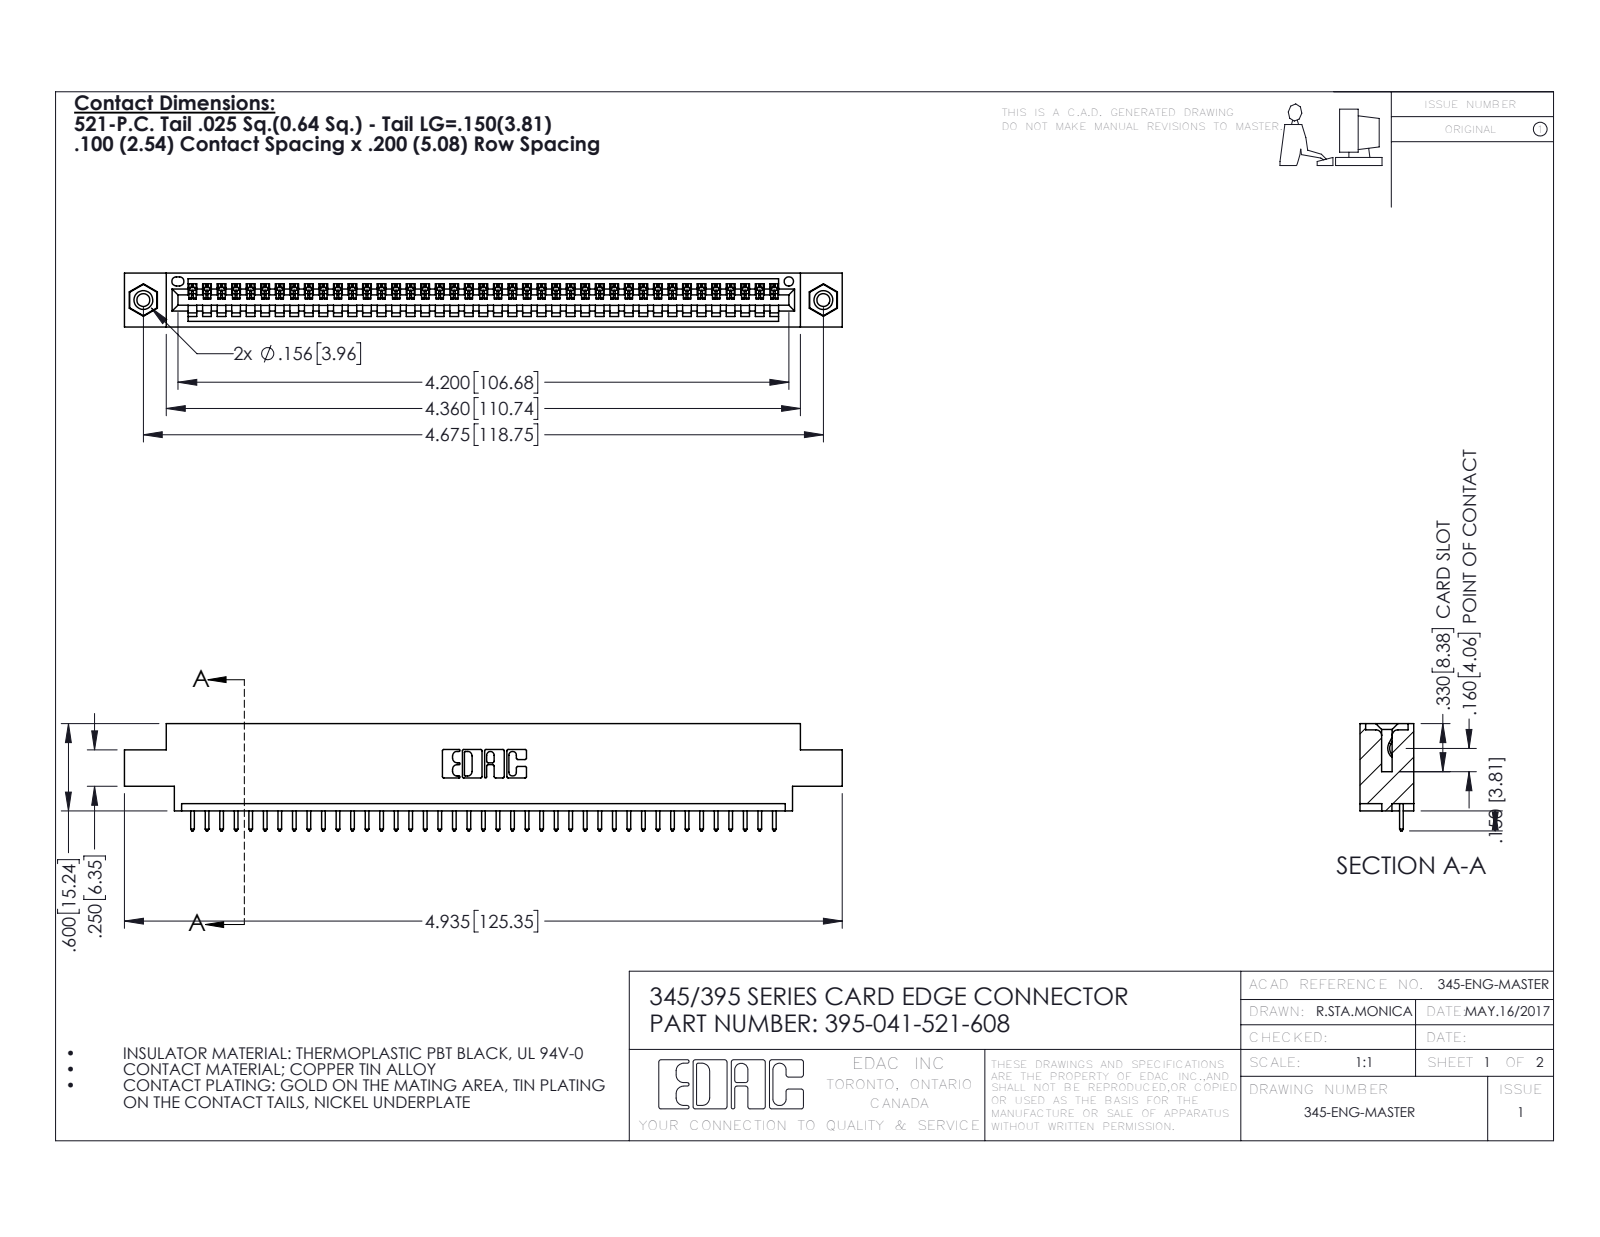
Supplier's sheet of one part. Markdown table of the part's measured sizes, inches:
| quantity | value |
| --- | --- |
| part name | 345-250-001_345-250-003-102; 395-041-521-608; 345 Part_0.170 Offset - 0.156 Dia-TI; 345-292-001_345-293-121 |
| STEP written by | SolidWorks 2016 (CONFIG_CONTROL_DESIGN) |
| units | inches |
| bodies | 44 solids, 2568 faces (1756 planar, 796 cylindrical, 16 other) |
| overall size | 4.935 × 0.737 × 0.37 |
| volume | 0.712 in³ |
| surface area | 23.52 in² |
| round holes (diameter × count) | 0.089 × 2, 0.125 × 2, 0.156 × 2, 0.064 × 1 |
| round bosses / shafts (diameter × count) | 0.155 × 2 |
| partial cylindrical surfaces (radius × count) | 0.006 × 82, 0.01 × 82, 0.01 × 22, 0.007 × 6, 0.031 × 6, 0.026 × 3, 0.031 × 2, 0.04 × 2 |
| main face-to-face distances | 0.072, 0.298, 0.37, 0.2, 0.098, 0.272, 0.025, 0.225, 0.175, 0.149 |
| hole center spacings | 0.27, 4.439, 4.675 |
